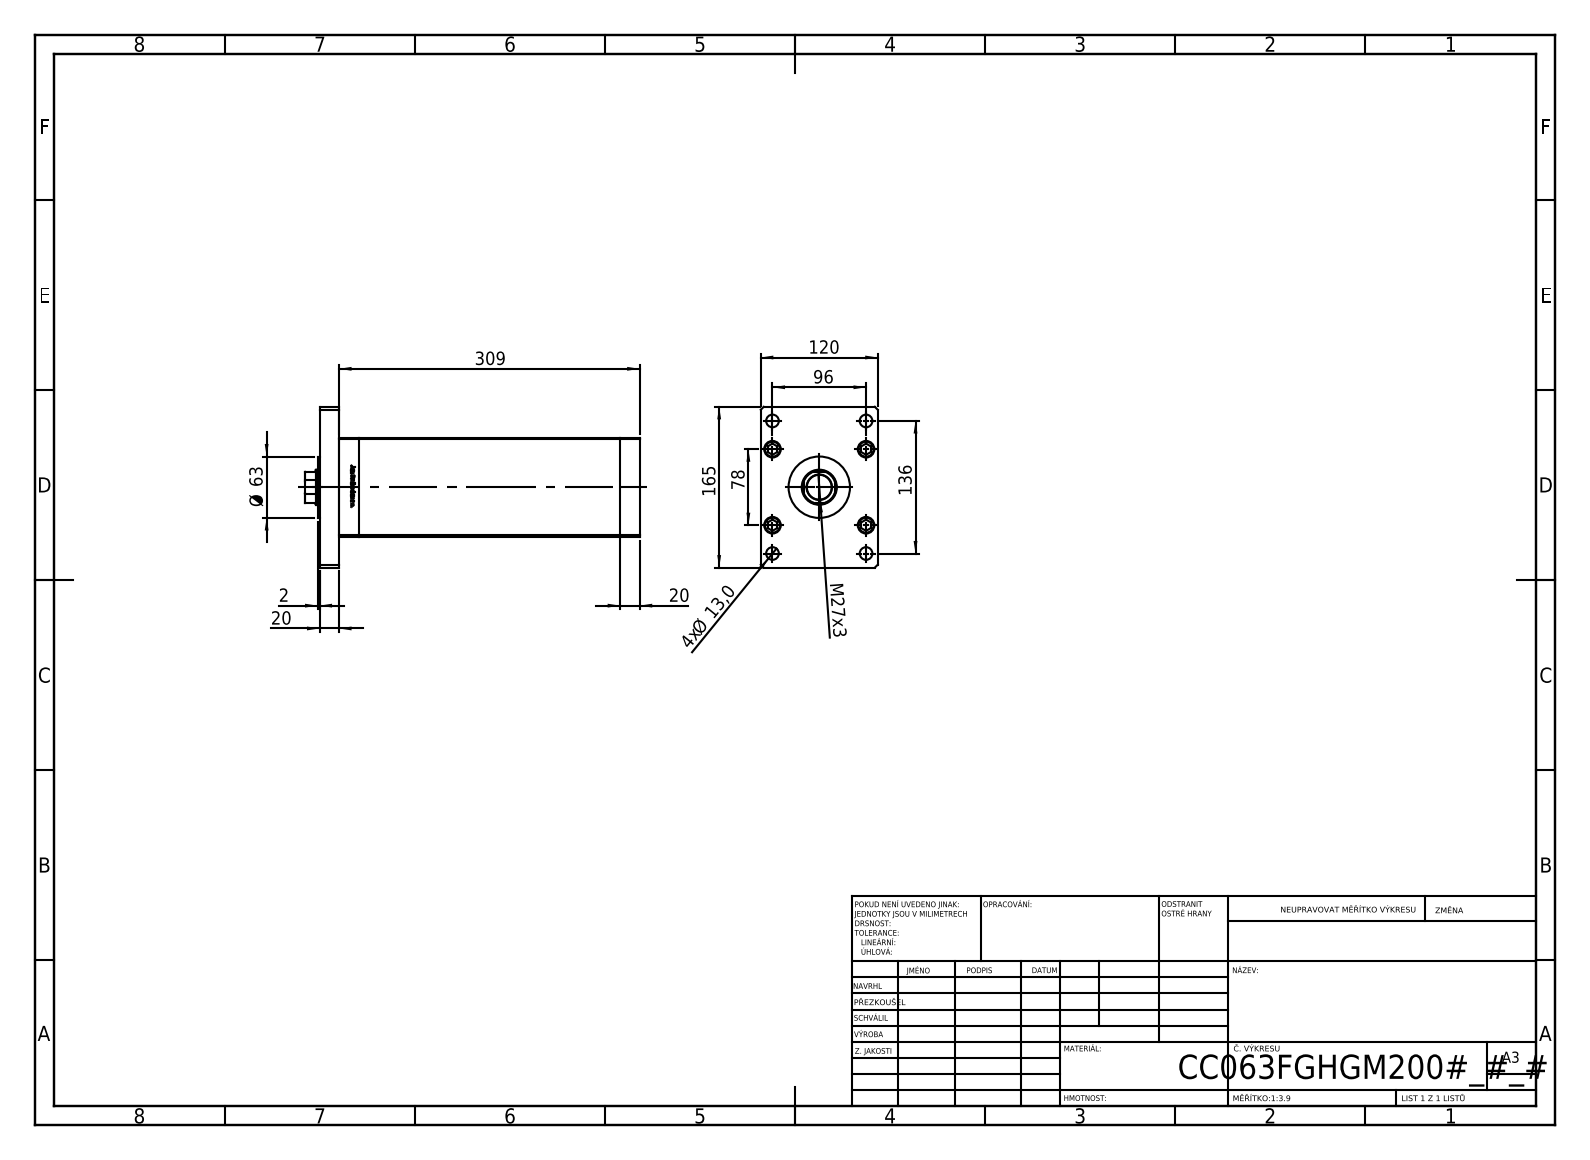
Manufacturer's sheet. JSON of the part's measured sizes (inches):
{"part_name": "V220C_F_MIDDLE; V220C_VC_F; V220C BACK_F; ALLEN BOLT (+2 more)", "step_written_by": "SolidWorks 2019 (CONFIG_CONTROL_DESIGN)", "units": "inches", "bodies": {"solids": 19, "faces": 1311, "planar": 517, "cylindrical": 188, "other": 606}, "overall_size": [13.524, 6.496, 4.724], "volume_in3": 220.2, "surface_area_in2": 642.3, "round_holes": [[0.531, 5], [0.709, 5], [0.472, 4], [0.512, 4], [0.669, 4], [0.079, 2], [0.518, 2], [1.004, 1], [1.417, 1], [1.476, 1]], "round_bosses_or_shafts": [[0.315, 9], [0.669, 5], [2.48, 1]], "partial_cylinders_radius": [[0.037, 2], [0.689, 1]], "face_to_face_distances": [0.787, 4.724, 4.016, 11.358, 12.146, 10.571, 1.575, 12.933, 1.348, 1.654], "hole_center_spacings": [1.634, 1.142, 2.435, 3.277, 3.78, 3.948, 4.213, 5.659]}
